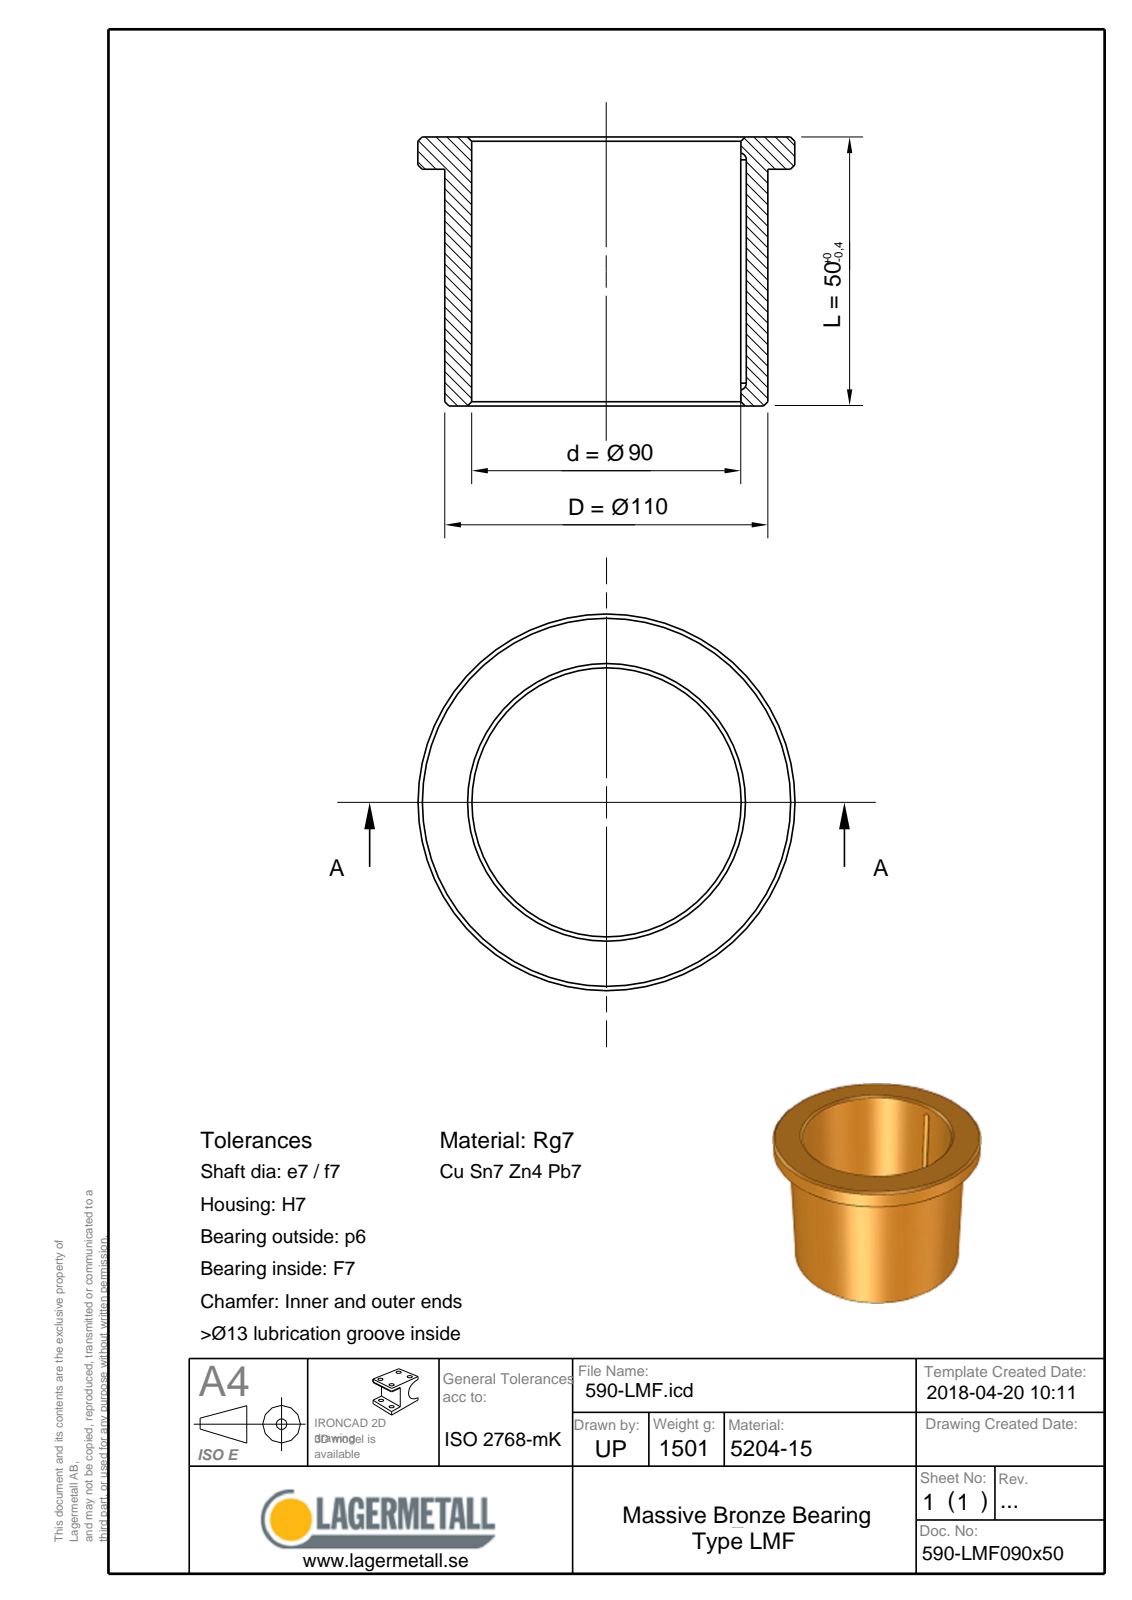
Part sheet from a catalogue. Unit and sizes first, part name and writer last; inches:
Units: inches
Overall size (bounding box): 4.724 × 4.724 × 1.969
Round holes (diameter × count): ⌀3.543 ×1
Round bosses / shafts (diameter × count): ⌀4.724 ×1, ⌀4.331 ×1
Partial cylindrical surfaces — rounded edges, fillets, slot ends (radius × count): R0.069 ×2
Main face-to-face distances: 1.969, 1.654, 0.315
Volume: 10.41 in³ · Surface area: 63.02 in²
Bodies: 1 solid, 16 faces (4 planar, 5 cylindrical, 7 other)
Part name (STEP PRODUCT): 590-LMF090x50
STEP written by: Spatial InterOp 3D (CONFIG_CONTROL_DESIGN)
